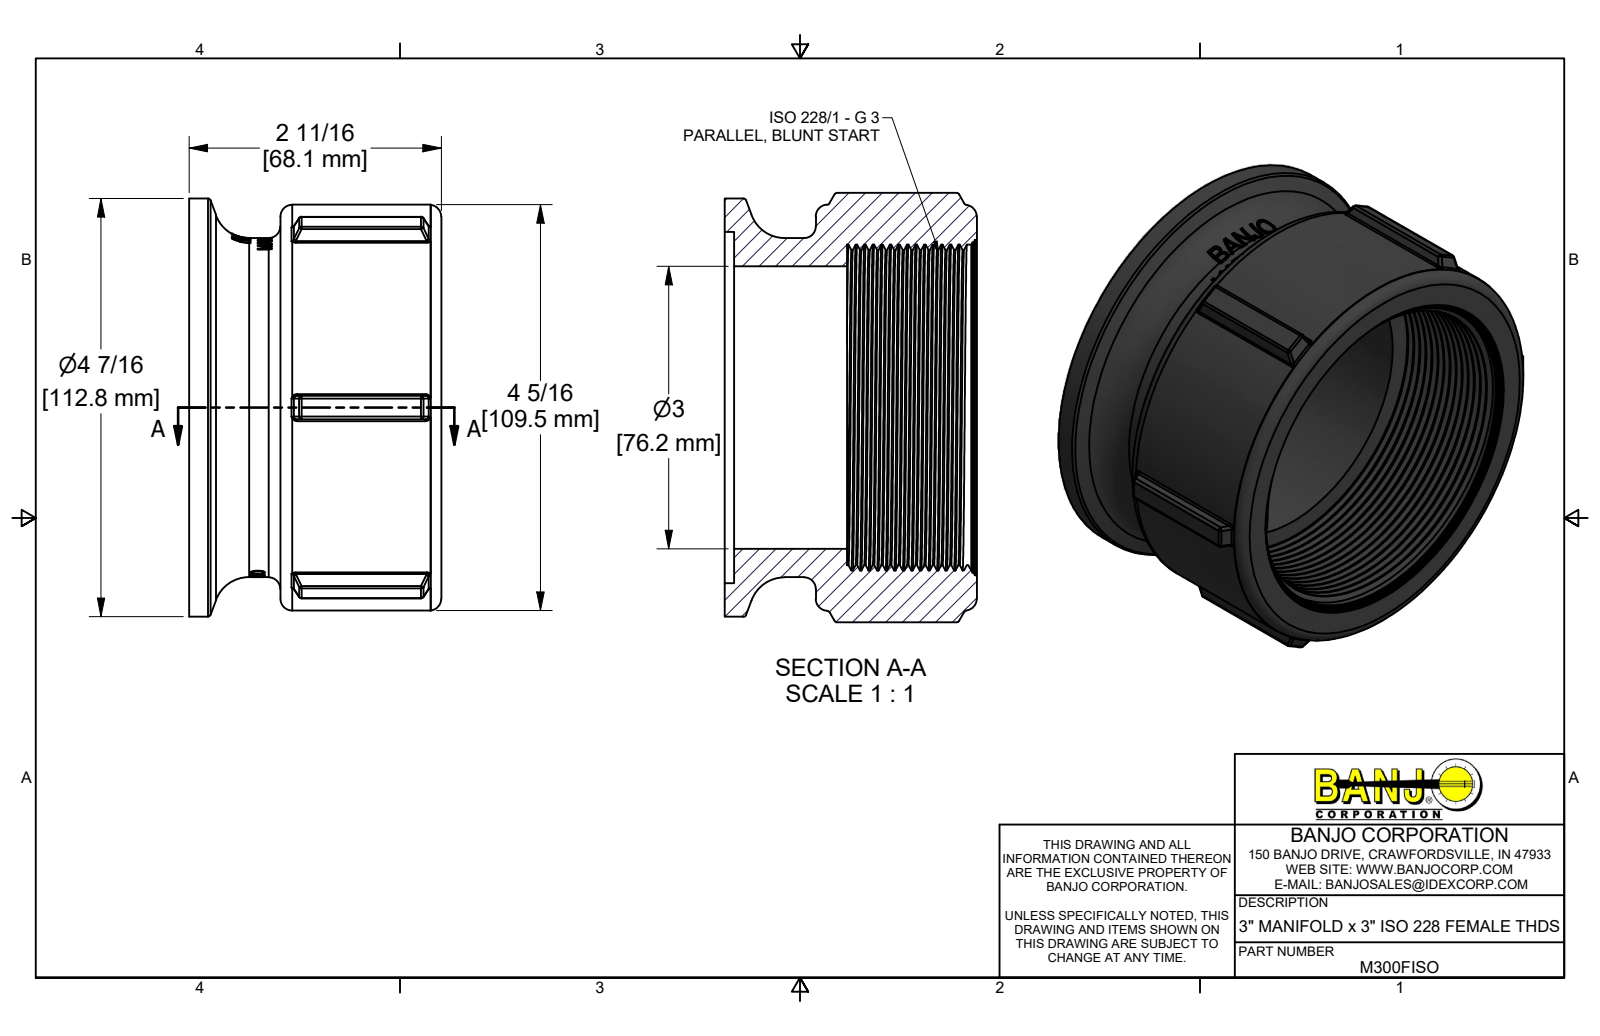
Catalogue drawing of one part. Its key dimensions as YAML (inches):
part_name: "M300FISO"
step_written_by: "Autodesk Inventor 2019 (AUTOMOTIVE_DESIGN)"
units: inches
bodies: {solids: 1, faces: 600, planar: 172, cylindrical: 113, other: 315}
overall_size: [4.56, 4.44, 2.68]
volume: 17.79
surface_area: 99.28
round_holes:
  - {diameter: 3, count: 1}
  - {diameter: 3.344, count: 1}
  - {diameter: 3.46, count: 1}
  - {diameter: 3.51, count: 1}
  - {diameter: 3.56, count: 1}
  - {diameter: 3.73, count: 1}
round_bosses_or_shafts:
  - {diameter: 4.44, count: 1}
  - {diameter: 4.31, count: 1}
  - {diameter: 3.6, count: 1}
partial_cylinders:
  - {radius: 0.02, count: 12}
  - {radius: 0.03, count: 12}
  - {radius: 0.923, count: 1}
  - {radius: 1.77, count: 1}
face_to_face_distances: [0.1, 2.58, 2.68, 1.38, 1.2, 1.3, 1.71, 0.33, 0.87, 0.97]
